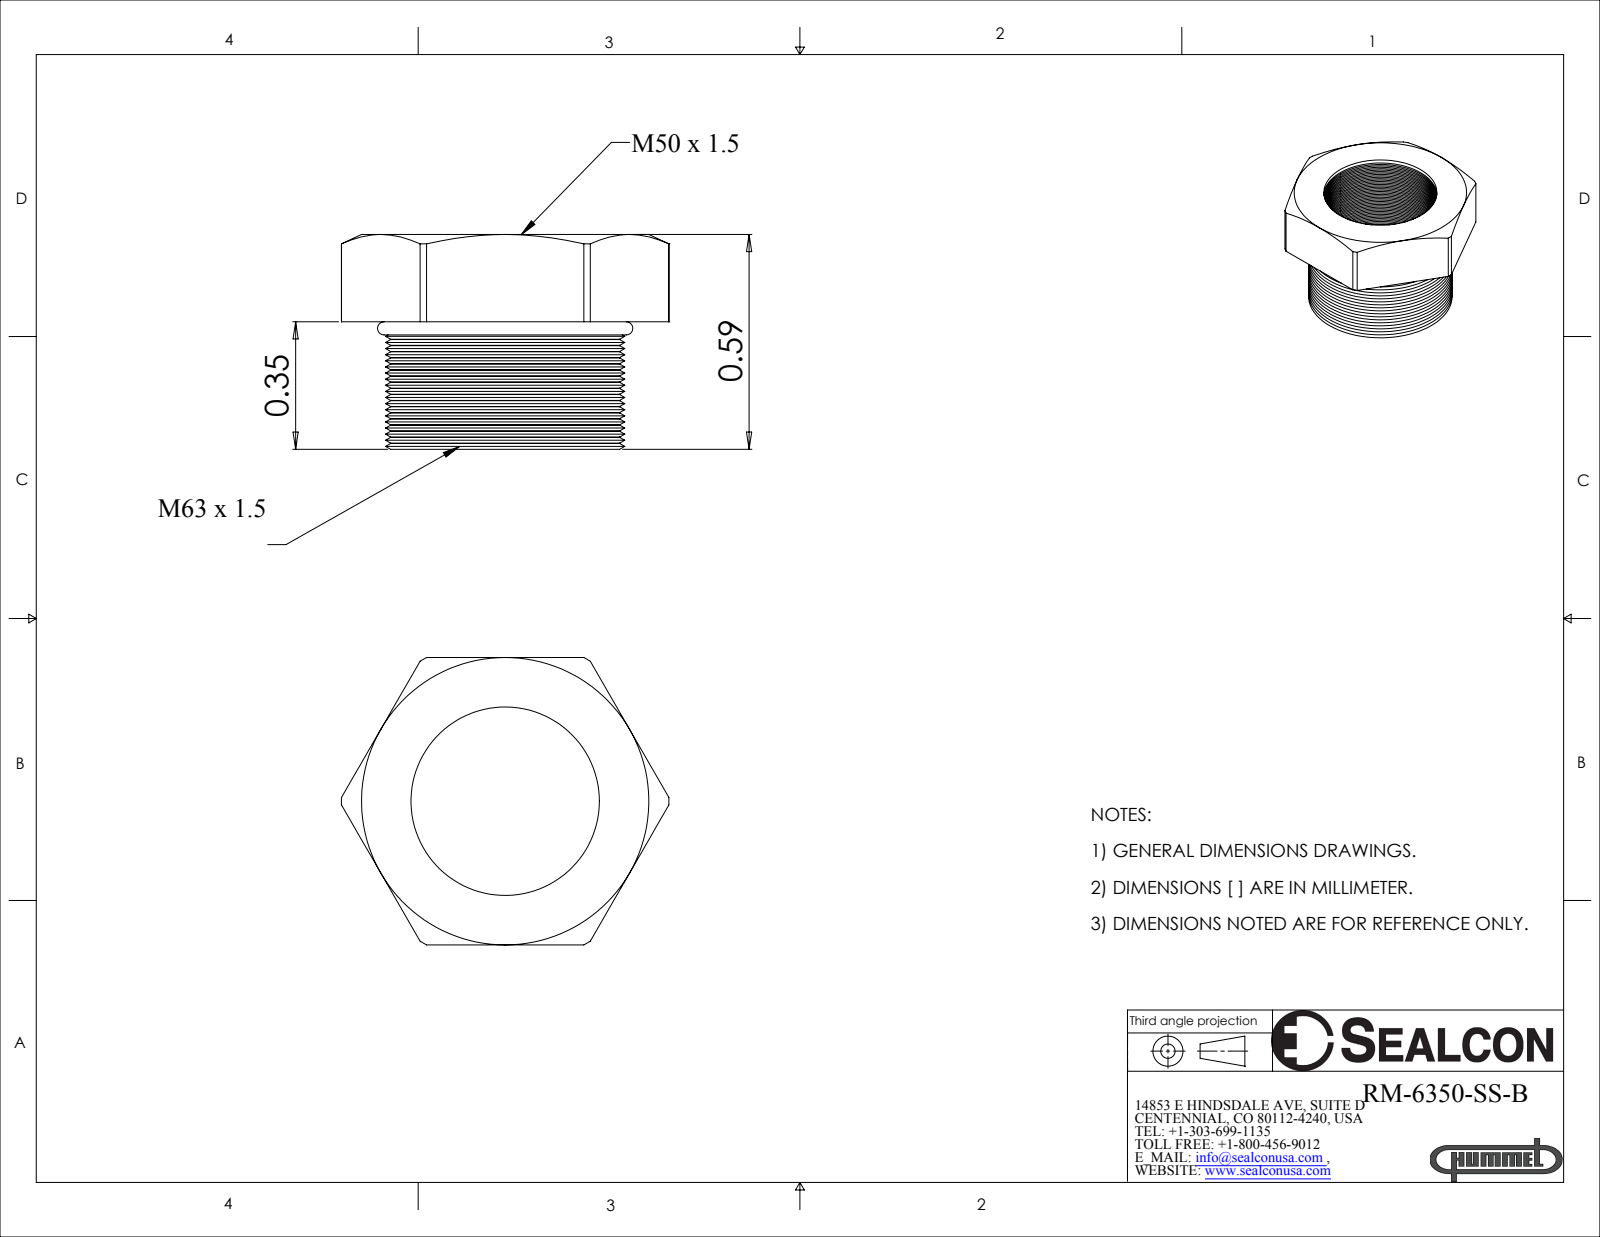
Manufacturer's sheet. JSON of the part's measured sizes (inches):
{"part_name": "RM-6350-SS-B", "step_written_by": "SolidWorks 2008 (CONFIG_CONTROL_DESIGN)", "units": "inches", "bodies": {"solids": 2, "faces": 361, "planar": 9, "cylindrical": 121, "other": 231}, "overall_size": [0.901, 0.79, 0.59], "volume_in3": 0.118, "surface_area_in2": 4.79, "round_holes": [[0.518, 1]], "round_bosses_or_shafts": [[0.63, 1]], "partial_cylinders_radius": [[0.45, 1]], "face_to_face_distances": [0.79, 0.24, 0.35, 0.59]}
